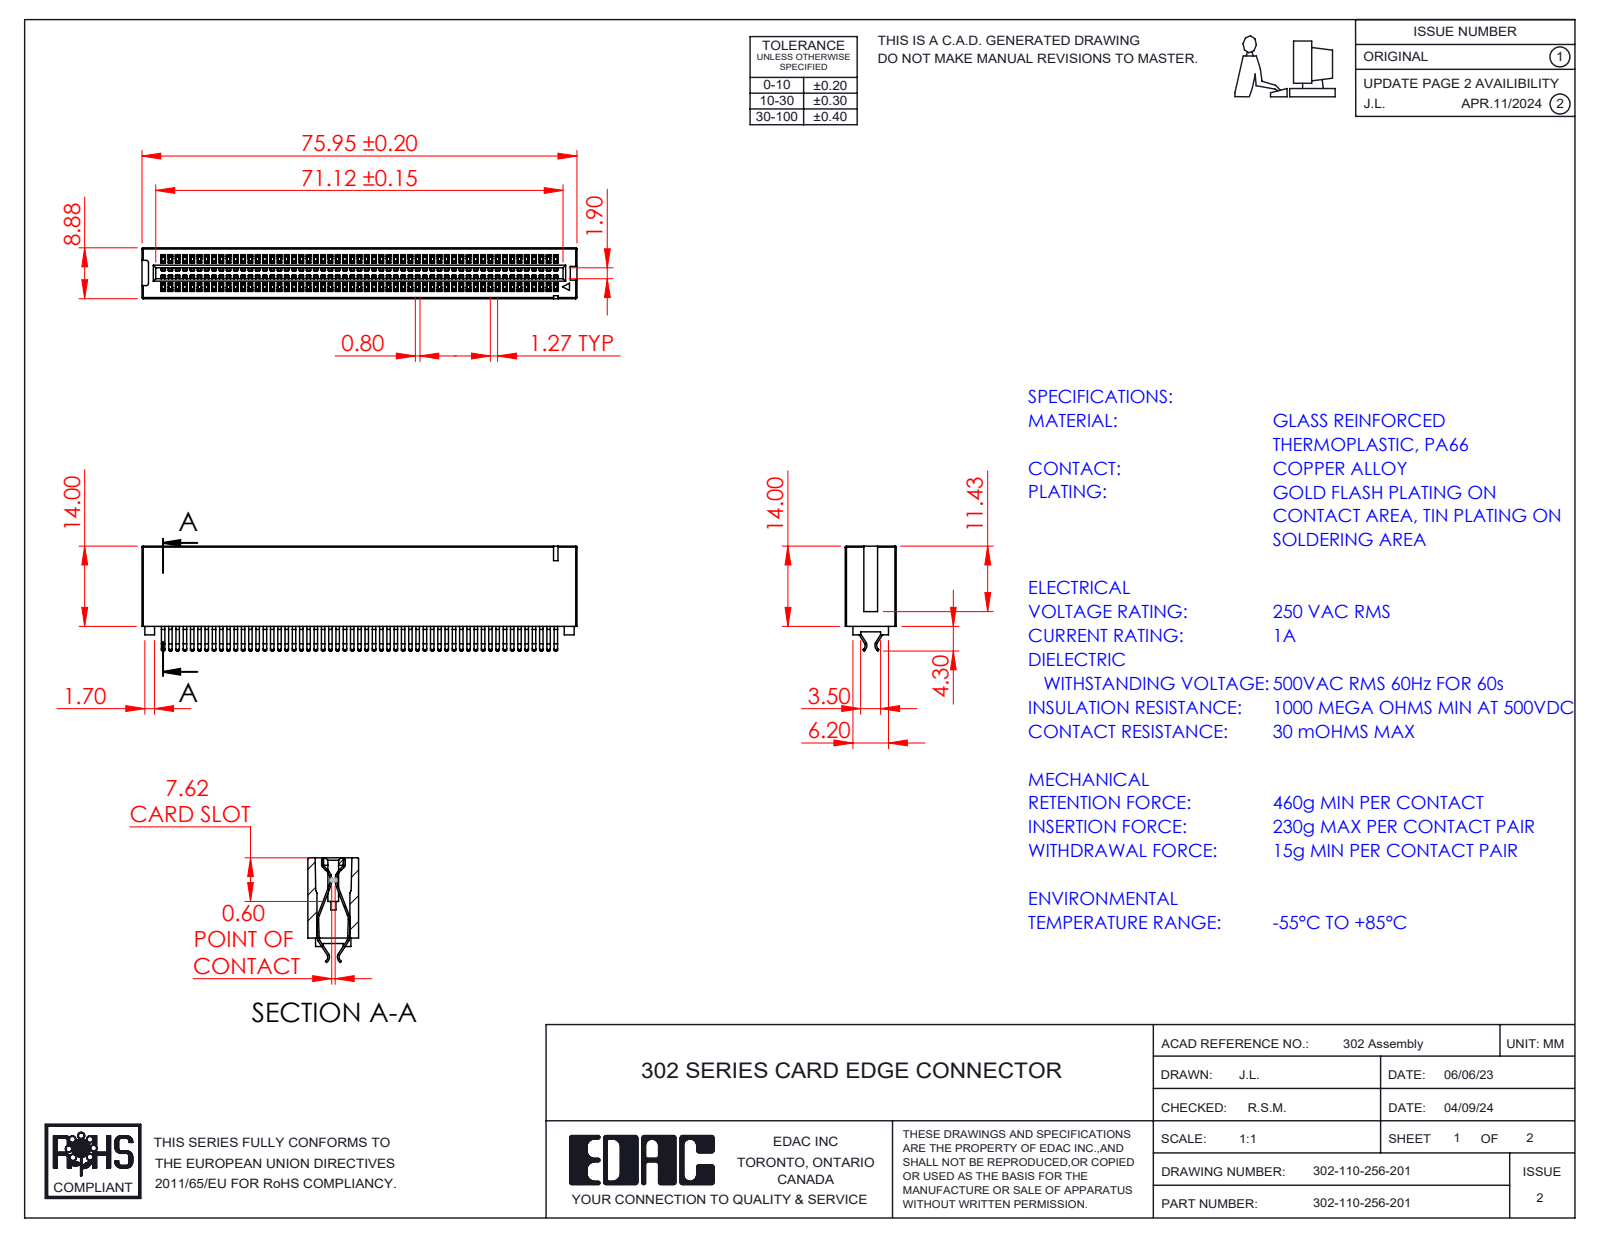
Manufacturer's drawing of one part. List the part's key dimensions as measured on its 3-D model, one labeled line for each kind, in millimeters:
Part name (STEP PRODUCT): 302-110-256-201; HSG_Vertical HSG; Contact_302-290-X56
STEP written by: SolidWorks 2023 (CONFIG_CONTROL_DESIGN)
Units: millimetres
Bodies: 111 solids, 5291 faces (3514 planar, 1773 cylindrical, 4 other)
Overall size (bounding box): 75.95 × 18.3 × 8.88
Volume: 5 808 mm³ · Surface area: 16 679 mm²
Partial cylindrical surfaces — rounded edges, fillets, slot ends (radius × count): R0.2 ×338, R0.11 ×2, R0.4 ×2, R0.41 ×2, R0.93 ×2, R1.05 ×2, R1.23 ×2, R1.25 ×2
Main face-to-face distances: 8.88, 1.27, 2.54, 3.81, 5.08, 7.62, 6.35, 8.89, 10.16, 1.9
